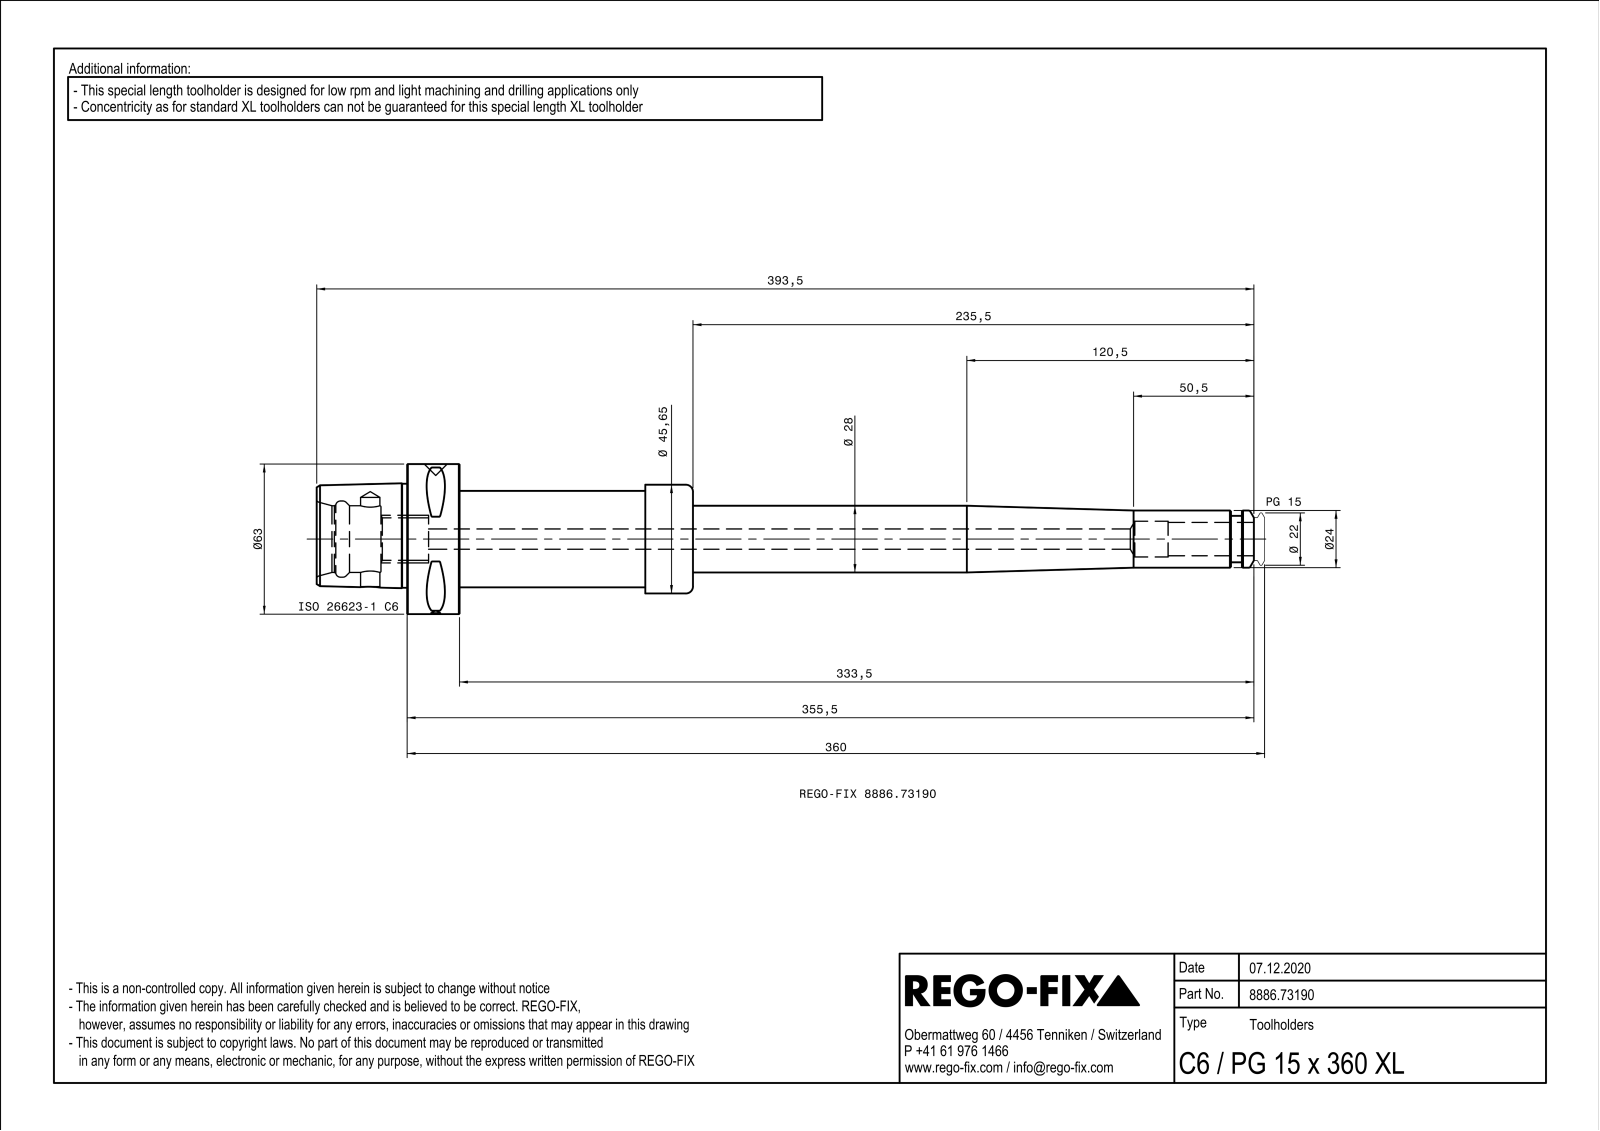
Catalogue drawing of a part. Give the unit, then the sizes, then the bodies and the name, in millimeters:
Units: millimetres
Overall size (bounding box): 393.5 × 63 × 63
Round holes (diameter × count): ⌀4 ×1, ⌀8.1 ×1, ⌀9 ×1, ⌀10 ×1, ⌀13 ×1, ⌀15 ×1, ⌀17.84 ×1, ⌀25 ×1, ⌀28 ×1, ⌀29 ×1, ⌀32 ×1, ⌀38.38 ×1
Round bosses / shafts (diameter × count): ⌀63 ×1, ⌀45.65 ×1, ⌀40.5 ×1, ⌀40 ×1, ⌀34 ×1, ⌀33 ×1, ⌀24.7 ×1, ⌀24 ×1
Partial cylindrical surfaces — rounded edges, fillets, slot ends (radius × count): R0.5 ×8, R22.77 ×1
Main face-to-face distances: 22, 98, 120, 6, 14, 158, 60, 38, 1.5, 96.5
Hole centre spacings: 27.5
Volume: 306 053 mm³ · Surface area: 72 897 mm²
Bodies: 1 solid, 175 faces (36 planar, 38 cylindrical, 101 other)
Part name (STEP PRODUCT): NOCUT
STEP written by: SIEMENS PLM Software Solid Edge ST10 (AUTOMOTIVE_DESIGN)
